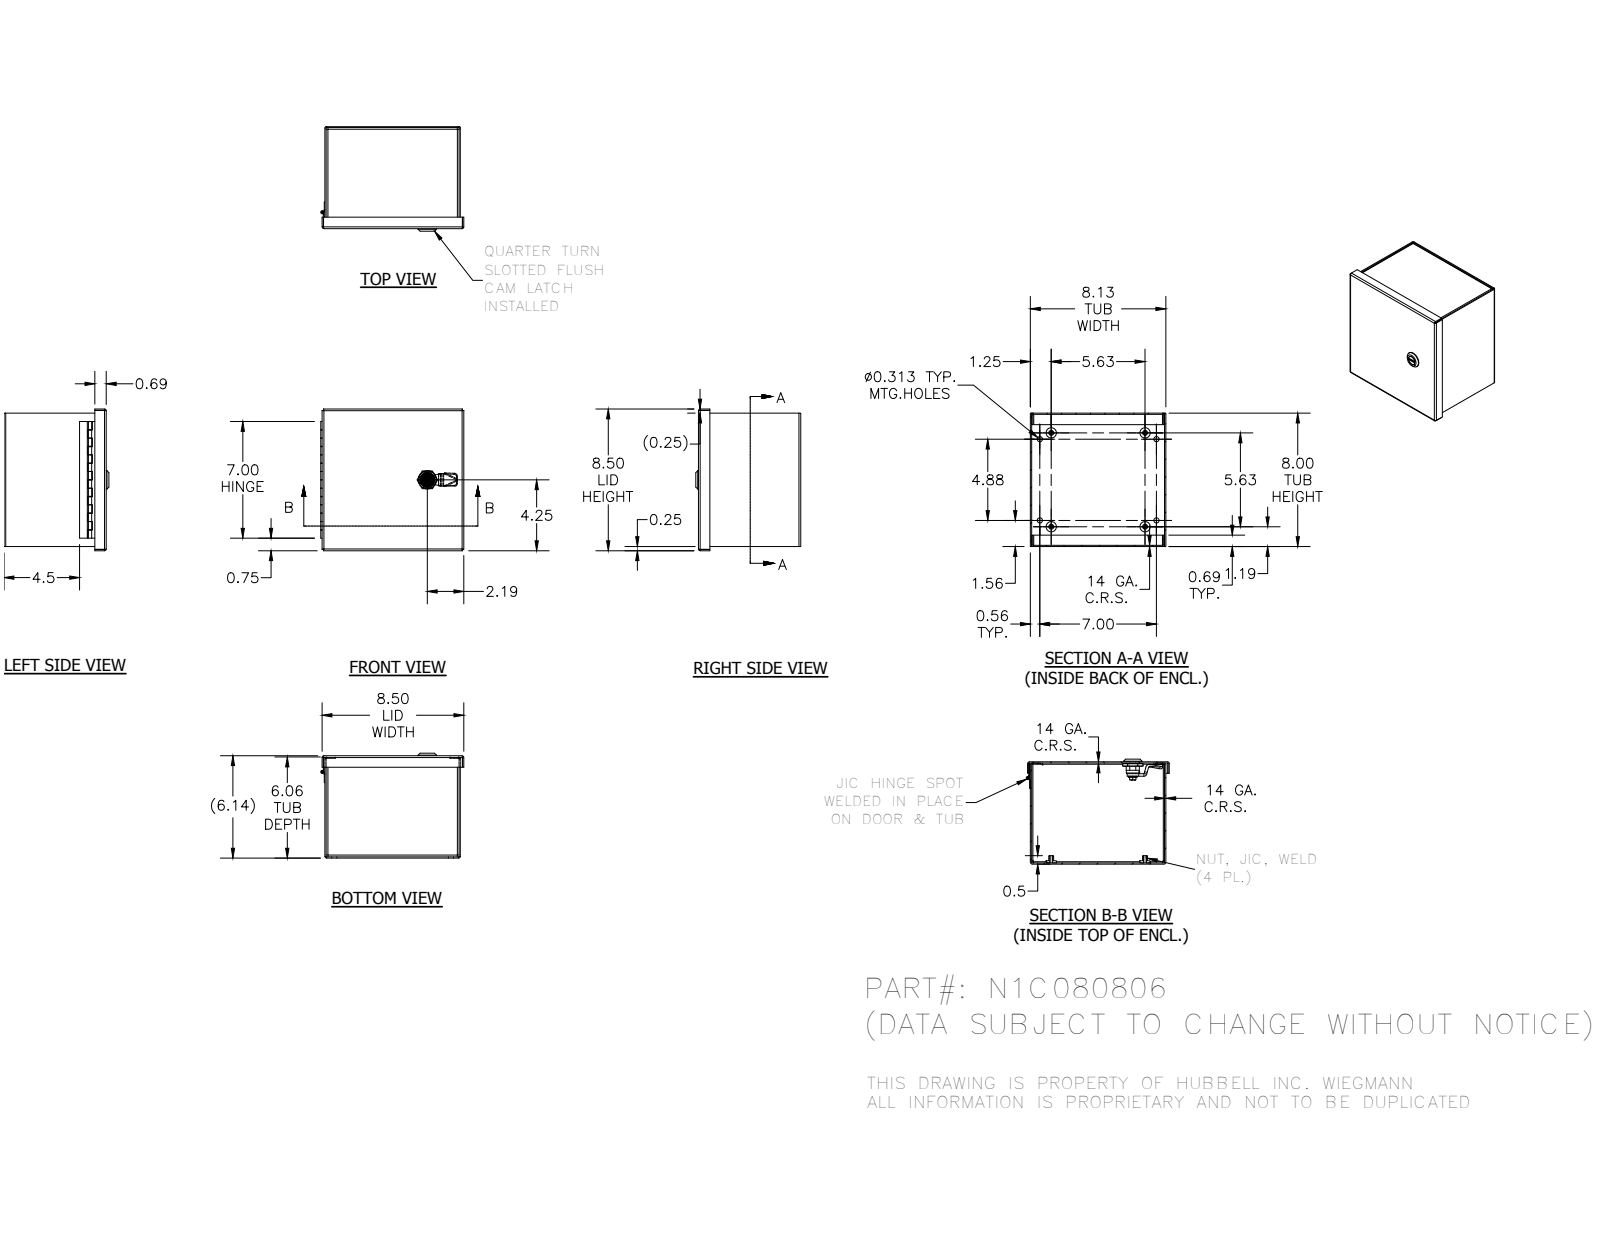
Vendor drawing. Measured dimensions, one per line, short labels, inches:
name: N1C_SMALL; N1C0806TB; N1C080806BLR; HFW3513 (+8 more)
written by: Autodesk Inventor 2012 (AUTOMOTIVE_DESIGN)
unit: in
bodies: 19 solids, 675 faces (387 planar, 206 cylindrical, 82 other)
size: 8.584 × 8.5 × 6.294
volume: 30.12 in³; area: 833.8 in²
holes: 4× ⌀0.156, 4× ⌀0.313, 1× ⌀0.116, 1× ⌀0.197, 1× ⌀0.315, 1× ⌀0.394, 1× ⌀0.402, 1× ⌀0.634, 1× ⌀0.802
bosses: 4× ⌀0.625, 4× ⌀0.3, 1× ⌀1.102, 1× ⌀0.866, 1× ⌀0.78, 1× ⌀0.63, 1× ⌀0.598, 1× ⌀0.531
rounds: 30× R0.012, 16× R0.031, 16× R0.105, 10× R0.02, 4× R0.157, 3× R0.016, 1× R0.039, 1× R0.173
face distances: 0.074, 6.063, 5.989, 8.051, 7.926, 7.977, 6.137, 8.125, 8, 7.852
hole spacings: 0.783, 5.295, 5.625, 6.324, 8.211, 2.82, 2.906, 4.875
